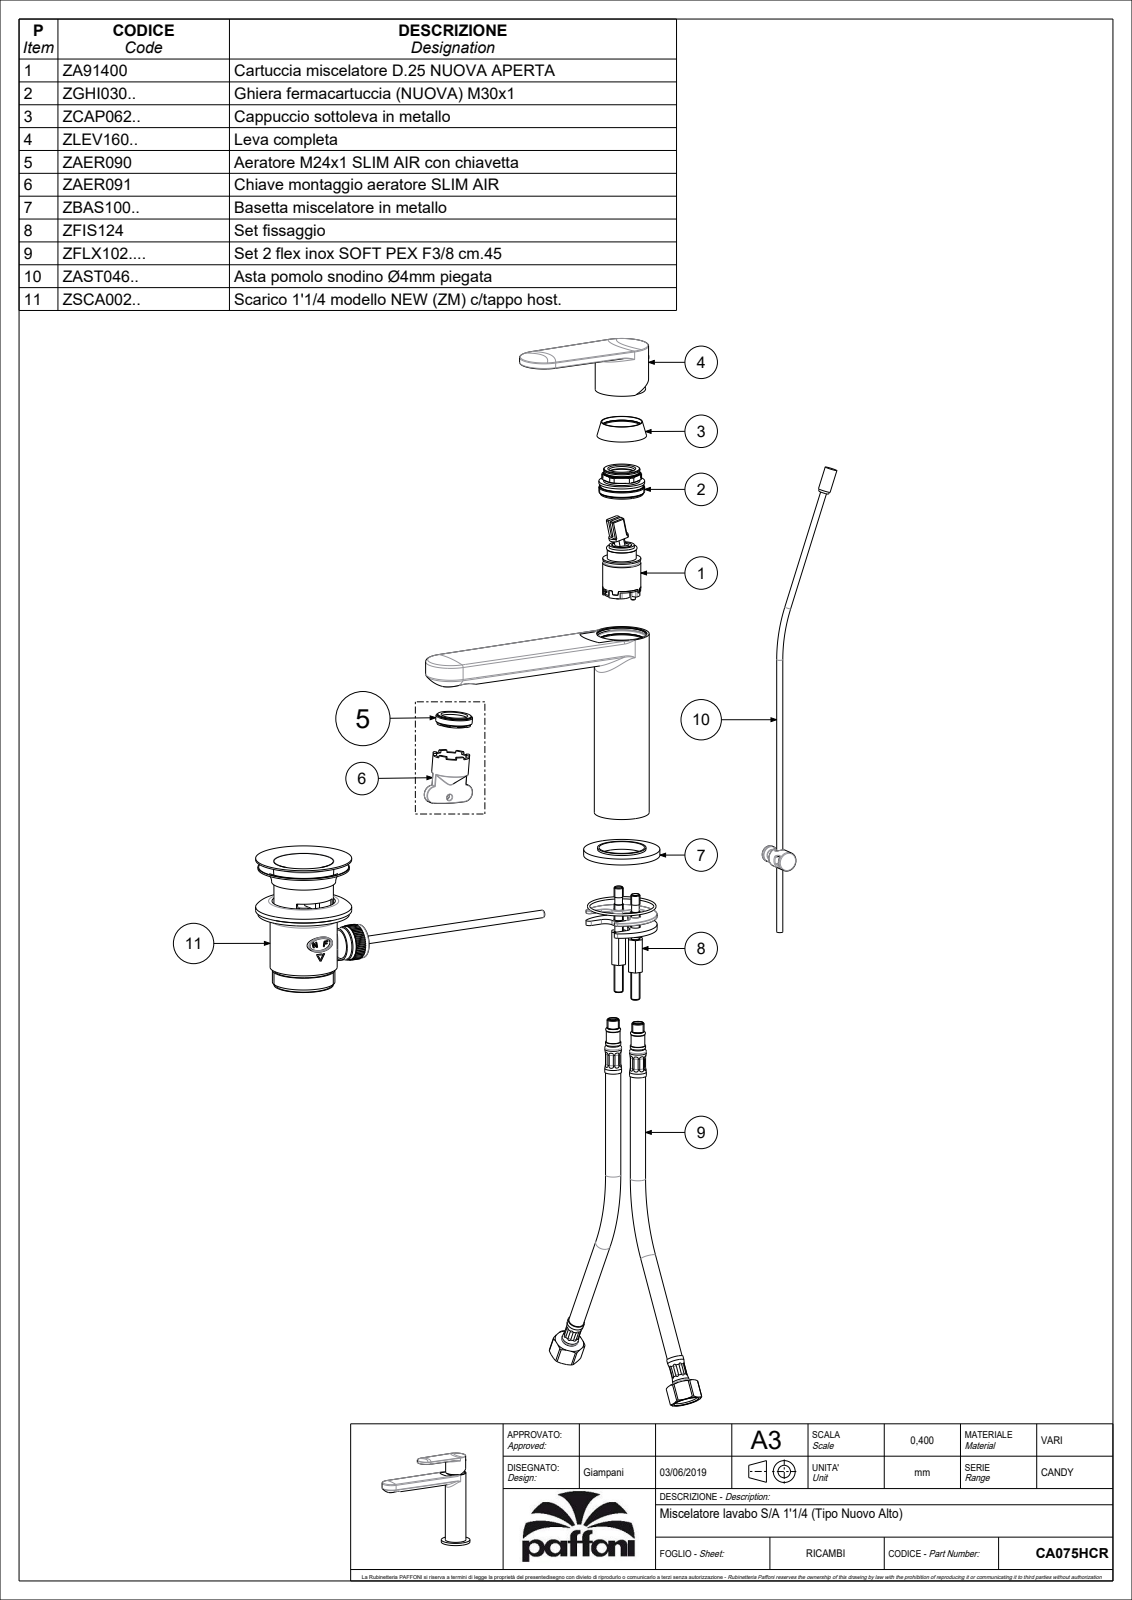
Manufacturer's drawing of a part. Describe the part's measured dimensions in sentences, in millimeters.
The part is named "CA075HCR". Its 3-D file was written by "CREO PARAMETRIC BY PTC INC, 2020044 (CONFIG_CONTROL_DESIGN)". It is 2 solids with 395 faces: 88 planar, 124 cylindrical and 183 other. Overall it measures 180.2 by 157.92 by 50 millimeters. Its volume is 100 827 cubic millimeters and its surface area 67 953 square millimeters. Round holes: 2 of diameter 5.5, 1 of diameter 3, 1 of diameter 4.2, 1 of diameter 4.5, 1 of diameter 5, 1 of diameter 16, 1 of diameter 17.5, 1 of diameter 24.5, 1 of diameter 24.8, 1 of diameter 26.2, 1 of diameter 28, 1 of diameter 29. Round bosses or shafts: 2 of diameter 35, 1 of diameter 50, 1 of diameter 31.8, 1 of diameter 24, 1 of diameter 18.5, 1 of diameter 8, 1 of diameter 7.6, 1 of diameter 5.5. Partial cylindrical surfaces (rounded edges, fillets, slot ends): 11 of radius 1, 8 of radius 0.5, 4 of radius 1.5, 4 of radius 3, 2 of radius 5, 2 of radius 16, 1 of radius 3.5, 1 of radius 9.75. The main face-to-face distances are 3, 4, 1.09, 2.91, 154.92, 153.83, 150.92, 2.5, 11.5, 125.5. The hole center spacings are 11.7, 13.04, 11, 22.
